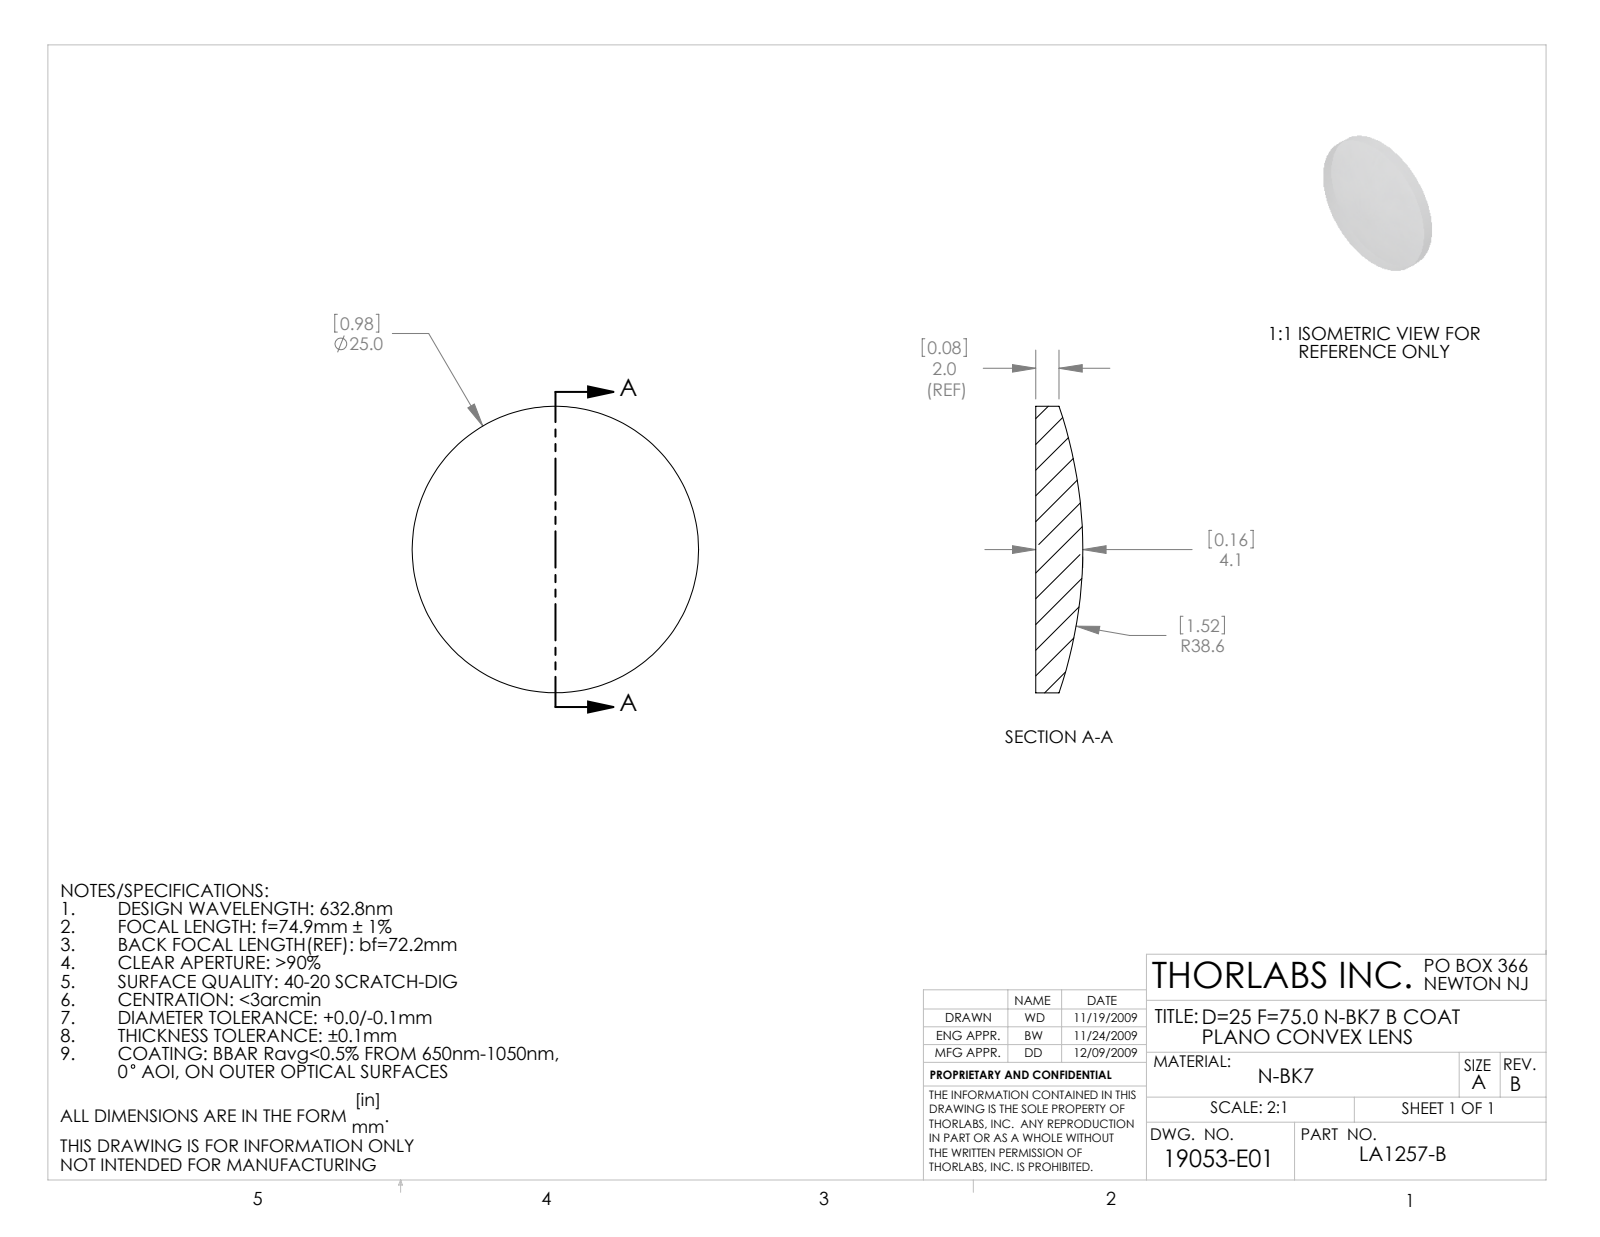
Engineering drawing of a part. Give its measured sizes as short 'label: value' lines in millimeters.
name: 19053-E0W
written by: SolidWorks 2009 (AUTOMOTIVE_DESIGN)
unit: mm
bodies: 1 solid, 5 faces (1 planar, 2 cylindrical, 2 other)
size: 25 × 25 × 4.1
volume: 1 507 mm³; area: 1 154 mm²
bosses: 1× ⌀25
